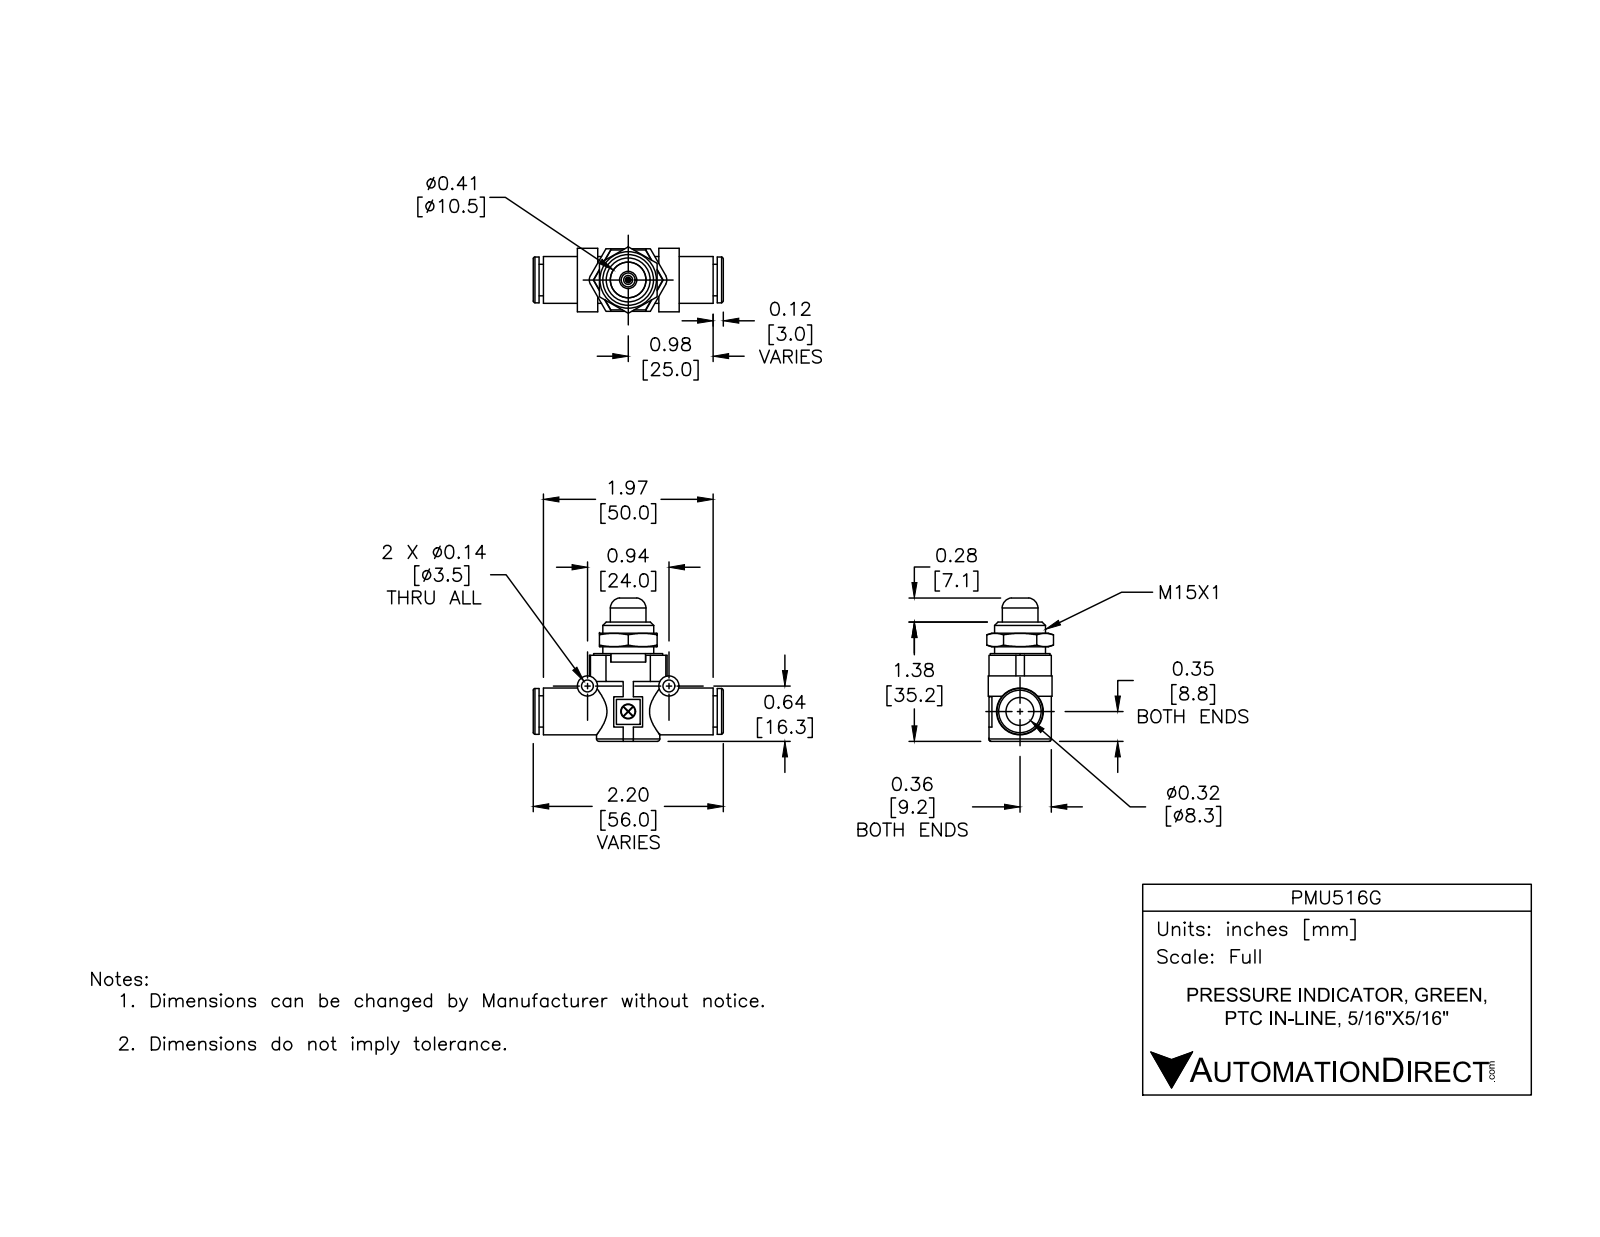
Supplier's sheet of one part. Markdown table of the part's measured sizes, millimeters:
| quantity | value |
| --- | --- |
| part name | PMU516G |
| STEP written by | SolidWorks 2015 (CONFIG_CONTROL_DESIGN) |
| units | millimeters |
| bodies | 7 solids, 175 faces (82 planar, 59 cylindrical, 34 other) |
| overall size | 56 × 42.24 × 19.63 |
| volume | 13 288 mm³ |
| surface area | 10 142 mm² |
| round holes (diameter × count) | 3.5 × 2, 0.71 × 1, 2.68 × 1, 4 × 1, 4.1 × 1, 8.25 × 1, 9.34 × 1, 9.4 × 1, 10.5 × 1 |
| round bosses / shafts (diameter × count) | 6 × 2, 18.65 × 1, 15 × 1, 13.8 × 1, 13.5 × 1, 10.49 × 1, 9.25 × 1, 4.4 × 1 |
| partial cylindrical surfaces (radius × count) | 0.75 × 2, 2.5 × 2 |
| main face-to-face distances | 8.5, 23.4, 1.75, 31.9, 27.9, 4.5, 4, 1.25, 2, 51.25 |
| hole center spacings | 14.15, 24 |
